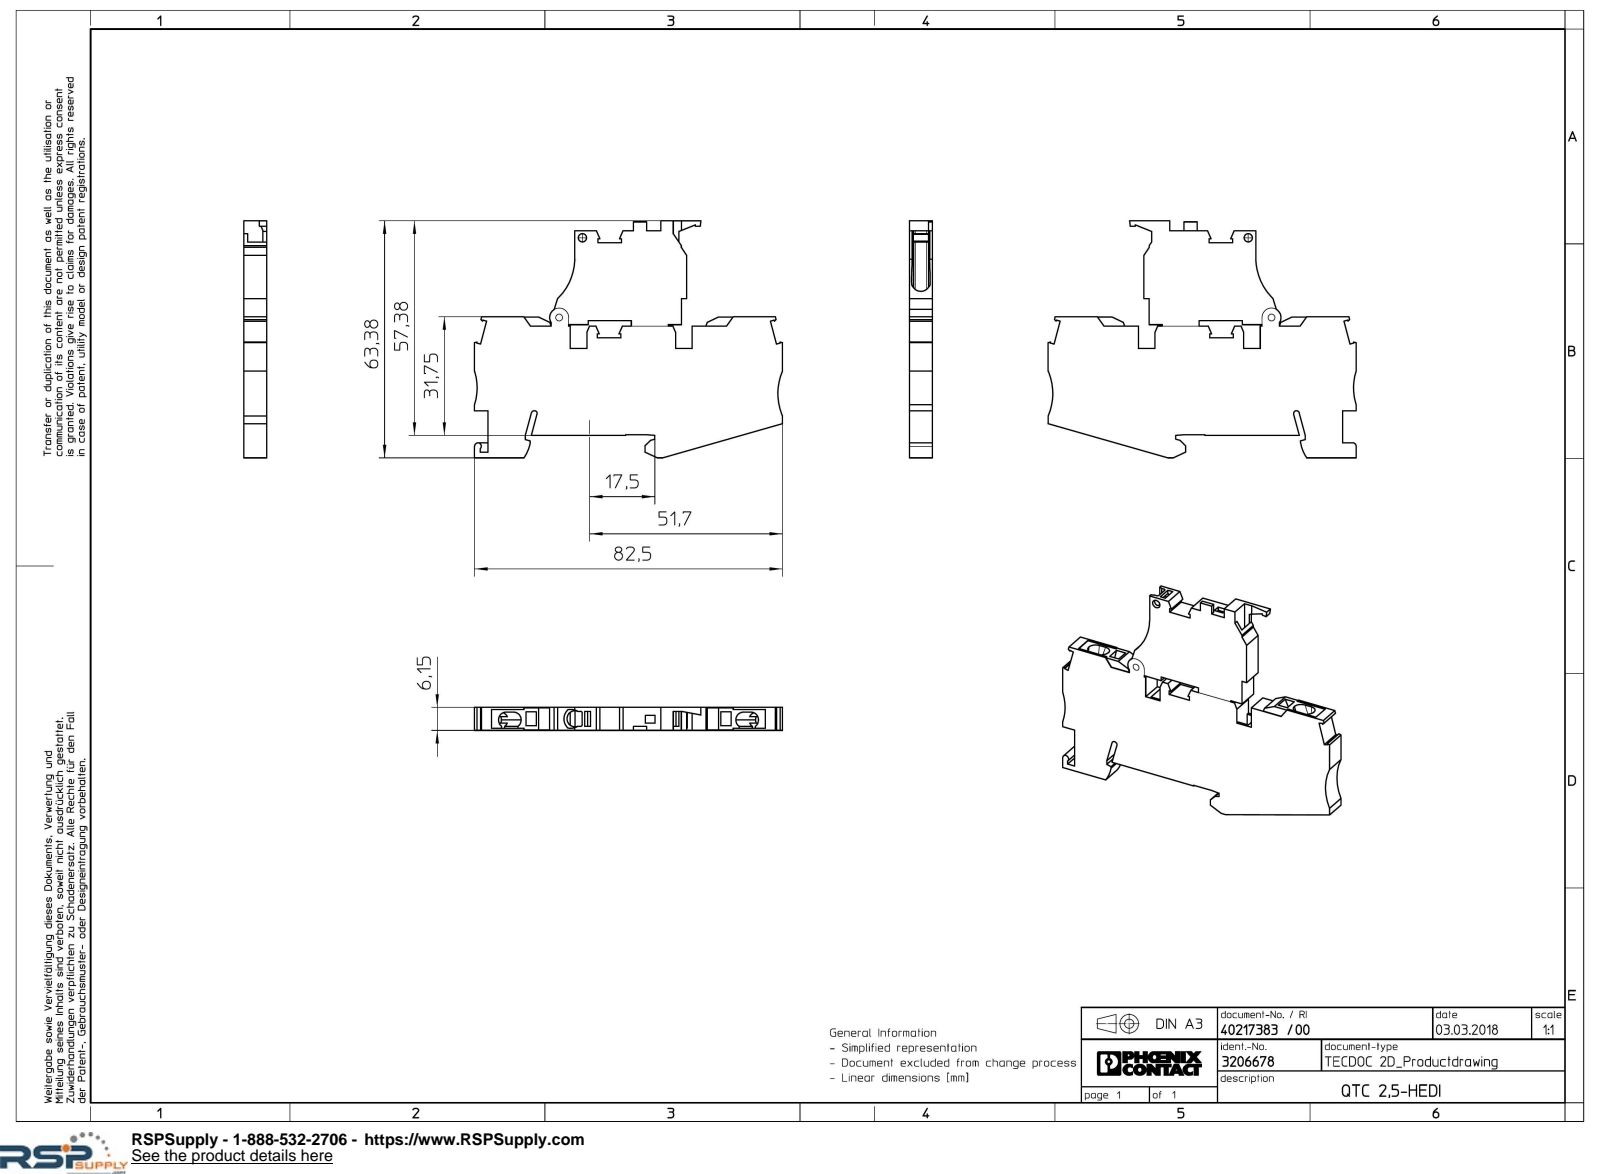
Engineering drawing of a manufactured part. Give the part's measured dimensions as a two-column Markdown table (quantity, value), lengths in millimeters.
| quantity | value |
| --- | --- |
| part name | QTC_2.5-HEDI-select |
| STEP written by | Creo Elements/Direct Modeling 20.1A 29-Sep-2018 (C) Parametric Technology GmbH (AUTOMOTIVE_DESIGN) |
| units | millimeters |
| bodies | 1 solid, 217 faces (190 planar, 26 cylindrical, 1 other) |
| overall size | 82.5 × 63.38 × 6.15 |
| volume | 18 658 mm³ |
| surface area | 10 568 mm² |
| round holes (diameter × count) | 2.25 × 1 |
| partial cylindrical surfaces (radius × count) | 2 × 8, 15 × 3, 0.5 × 2, 1.8 × 2, 3.95 × 2, 0.7 × 1, 0.8 × 1, 0.9 × 1 |
| main face-to-face distances | 6.15, 4.45, 0.65, 0.6, 1.05, 0.95, 5.5, 3.15, 29.25, 1.25 |
